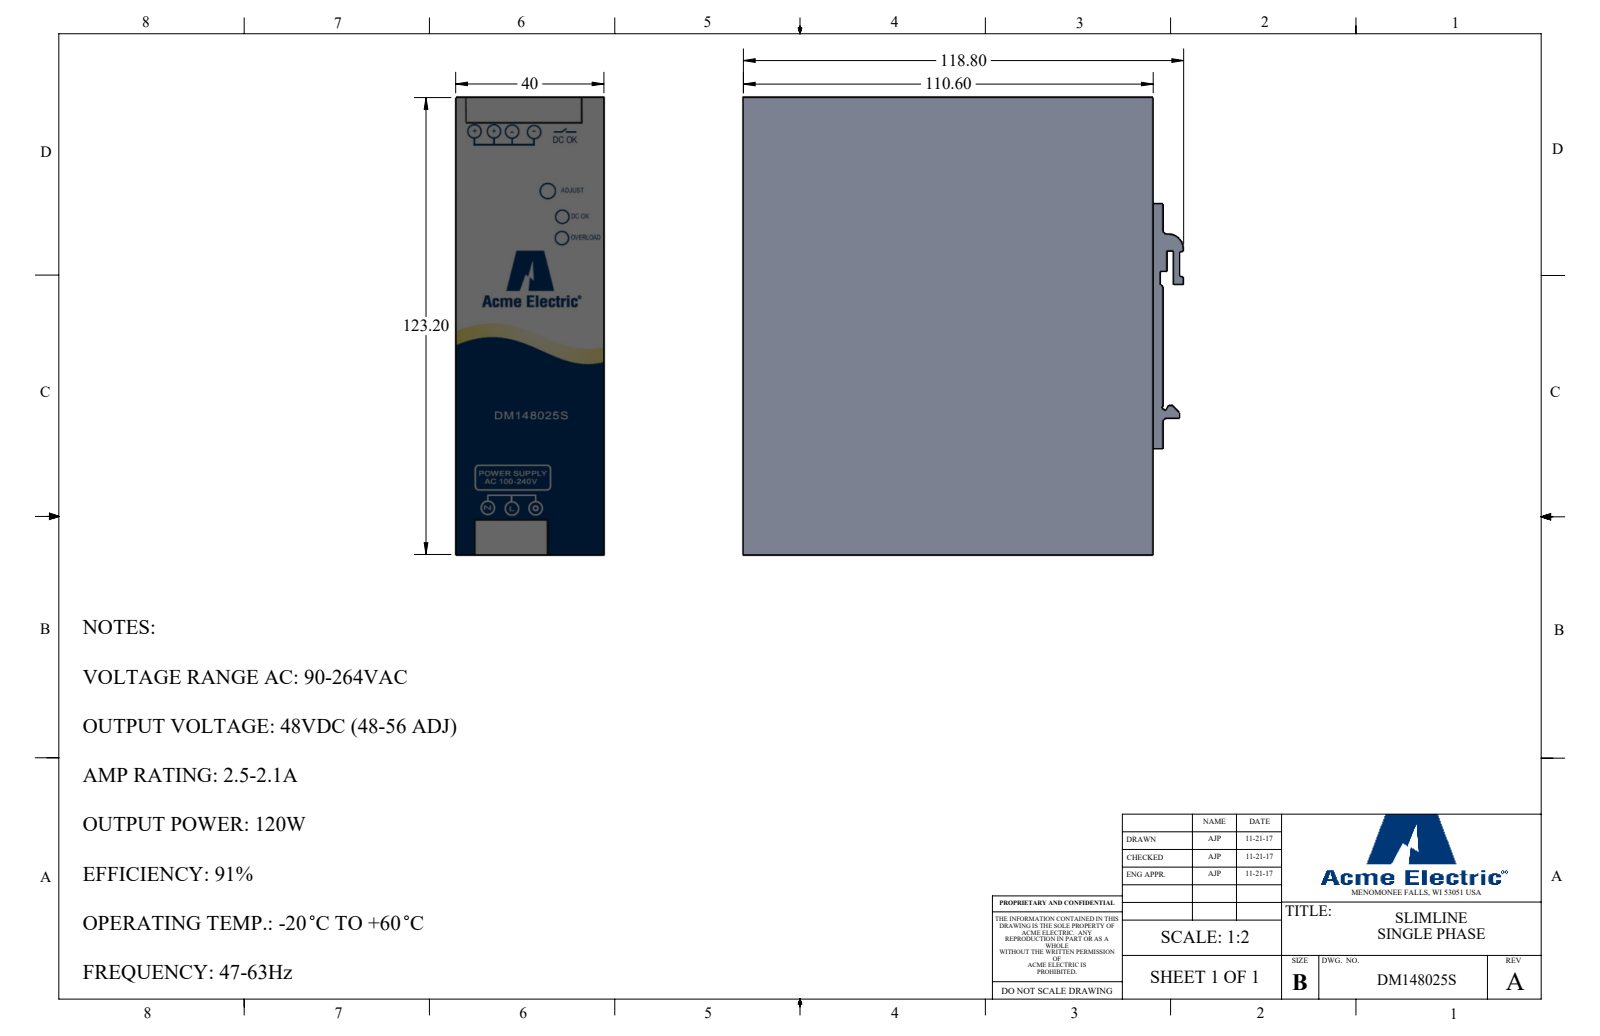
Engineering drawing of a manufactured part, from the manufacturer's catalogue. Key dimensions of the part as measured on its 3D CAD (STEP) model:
Part name (STEP PRODUCT): DM148025S
STEP written by: SolidWorks 2017 (AUTOMOTIVE_DESIGN)
Units: millimetres
Bodies: 1 solid, 36 faces (33 planar, 3 cylindrical, 0 other)
Overall size (bounding box): 123.2 × 118.8 × 40
Volume: 552 051 mm³ · Surface area: 47 758 mm²
Partial cylindrical surfaces — rounded edges, fillets, slot ends (radius × count): R1 ×2, R4 ×1
Main face-to-face distances: 40, 123.2, 110.6, 2.7, 113.3, 5, 35, 2.75, 5.45, 116.05
